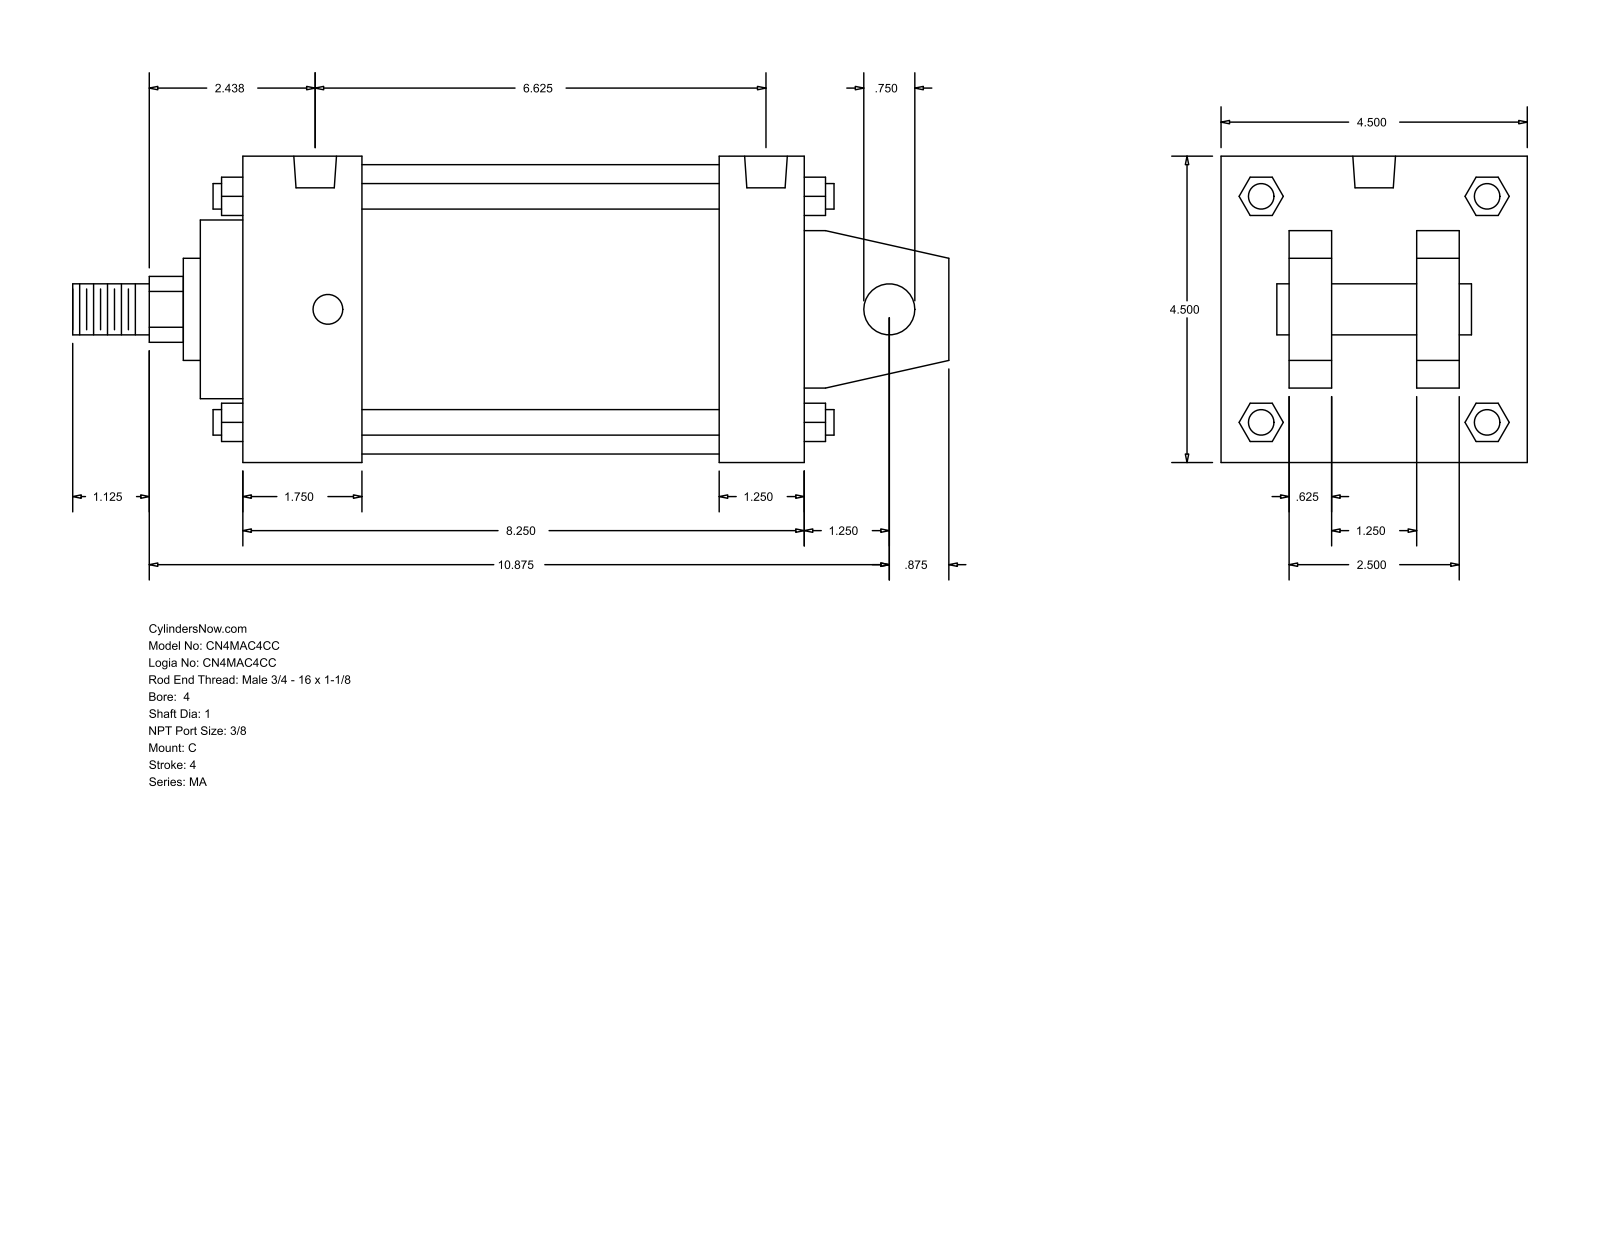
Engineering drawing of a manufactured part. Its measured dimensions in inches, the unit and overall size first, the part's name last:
Units: inches
Overall size (bounding box): 12.875 × 4.5 × 4.5
Round holes (diameter × count): ⌀0.437 ×4, ⌀0.627 ×2
Round bosses / shafts (diameter × count): ⌀0.375 ×4, ⌀0.75 ×2, ⌀4.25 ×1, ⌀2.625 ×1, ⌀1.5 ×1, ⌀1 ×1
Partial cylindrical surfaces — rounded edges, fillets, slot ends (radius × count): R0.484 ×1
Main face-to-face distances: 4.5, 8.25, 0.625, 2.875, 1.625, 1, 3.5, 1.875, 7, 1.25
Hole centre spacings: 0.187, 6.25, 6.438, 6.625
Bodies: 0 solids, 141 faces (109 planar, 32 cylindrical, 0 other)
Part name (STEP PRODUCT): MA_C__0400_1
STEP written by: GSSL Pune (CONFIG_CONTROL_DESIGN)
